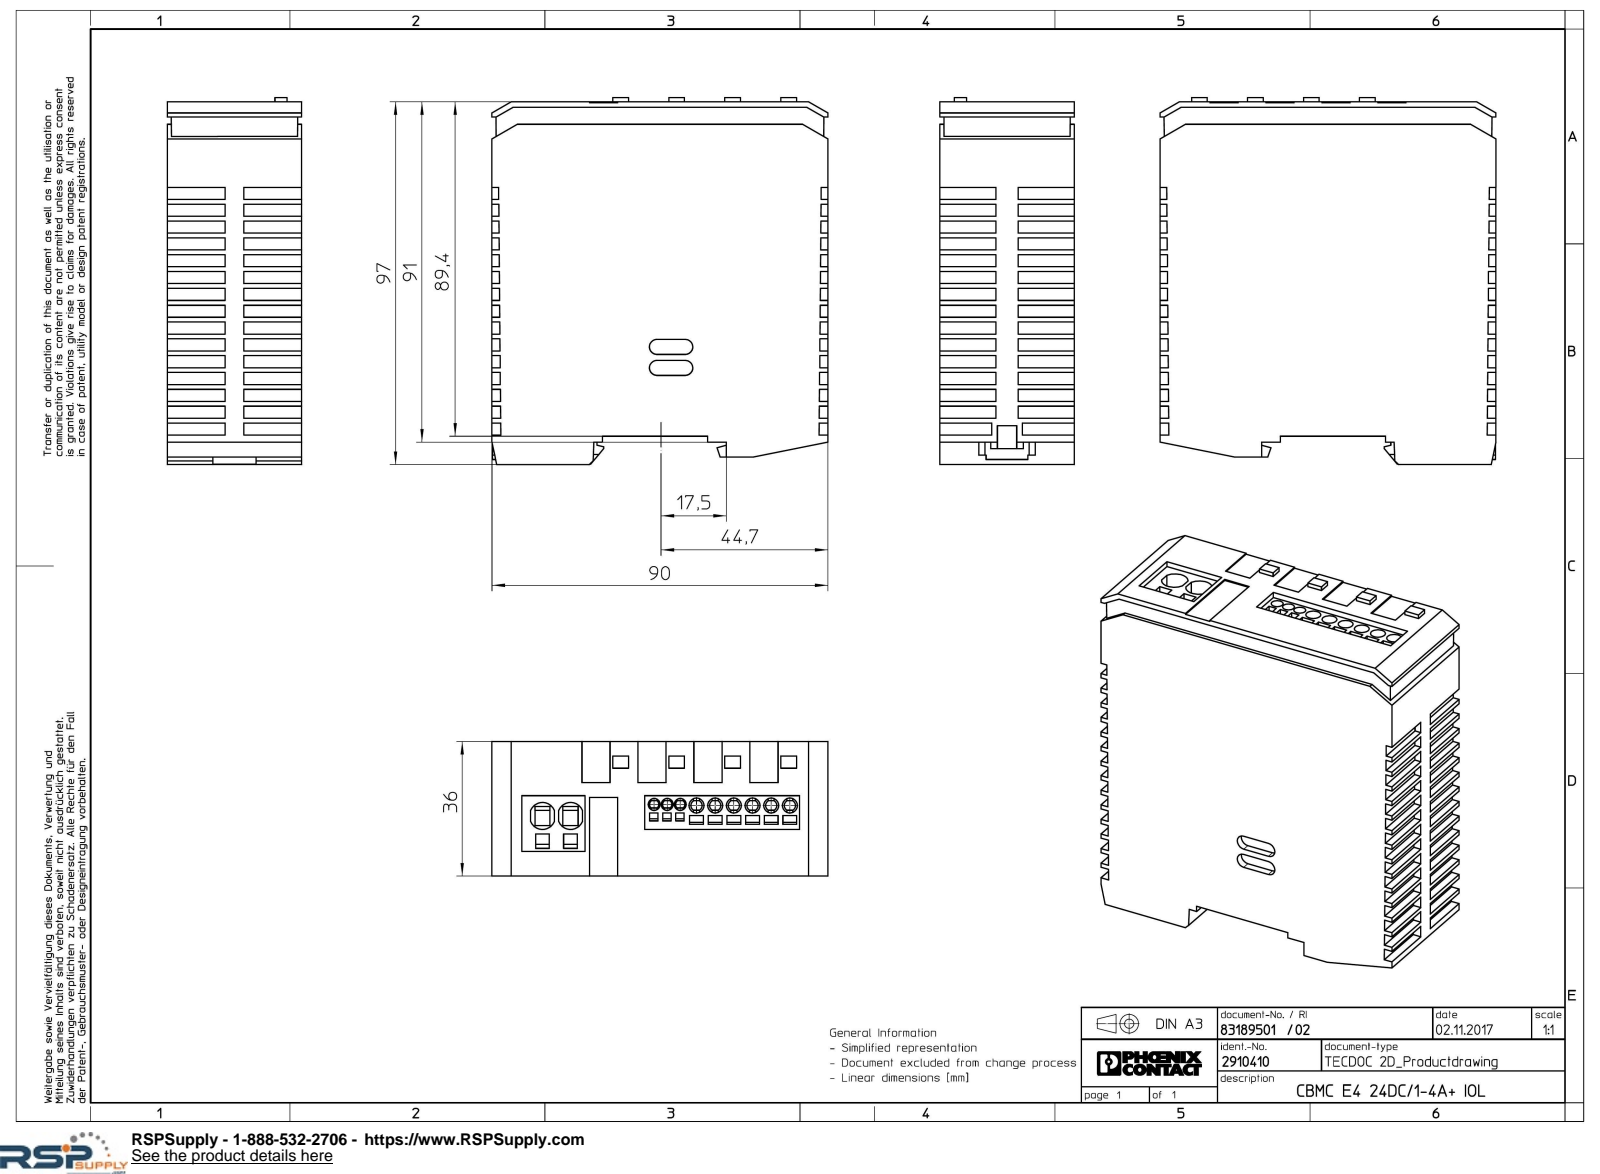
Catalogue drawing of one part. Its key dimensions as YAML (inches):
part_name: "CBMC_E4_24DC...IOL-select"
step_written_by: "Creo Elements/Direct Modeling 20.1A 29-Sep-2018 (C) Parametric Technology GmbH (AUTOMOTIVE_DESIGN)"
units: inches
bodies: {solids: 1, faces: 551, planar: 499, cylindrical: 24, other: 28}
overall_size: [3.862, 3.543, 1.417]
volume: 17.73
surface_area: 56.43
round_holes:
  - {diameter: 0.157, count: 6}
  - {diameter: 0.126, count: 3}
partial_cylinders:
  - {radius: 0.136, count: 4}
  - {radius: 0.472, count: 1}
face_to_face_distances: [1.417, 3.543, 3.52, 0.177, 0.299, 3.819, 0.354, 0.128, 0.05, 3.807]
hole_center_spacings: [0.197, 0.394, 0.591, 0.138, 0.787, 0.172, 0.276, 0.309]
